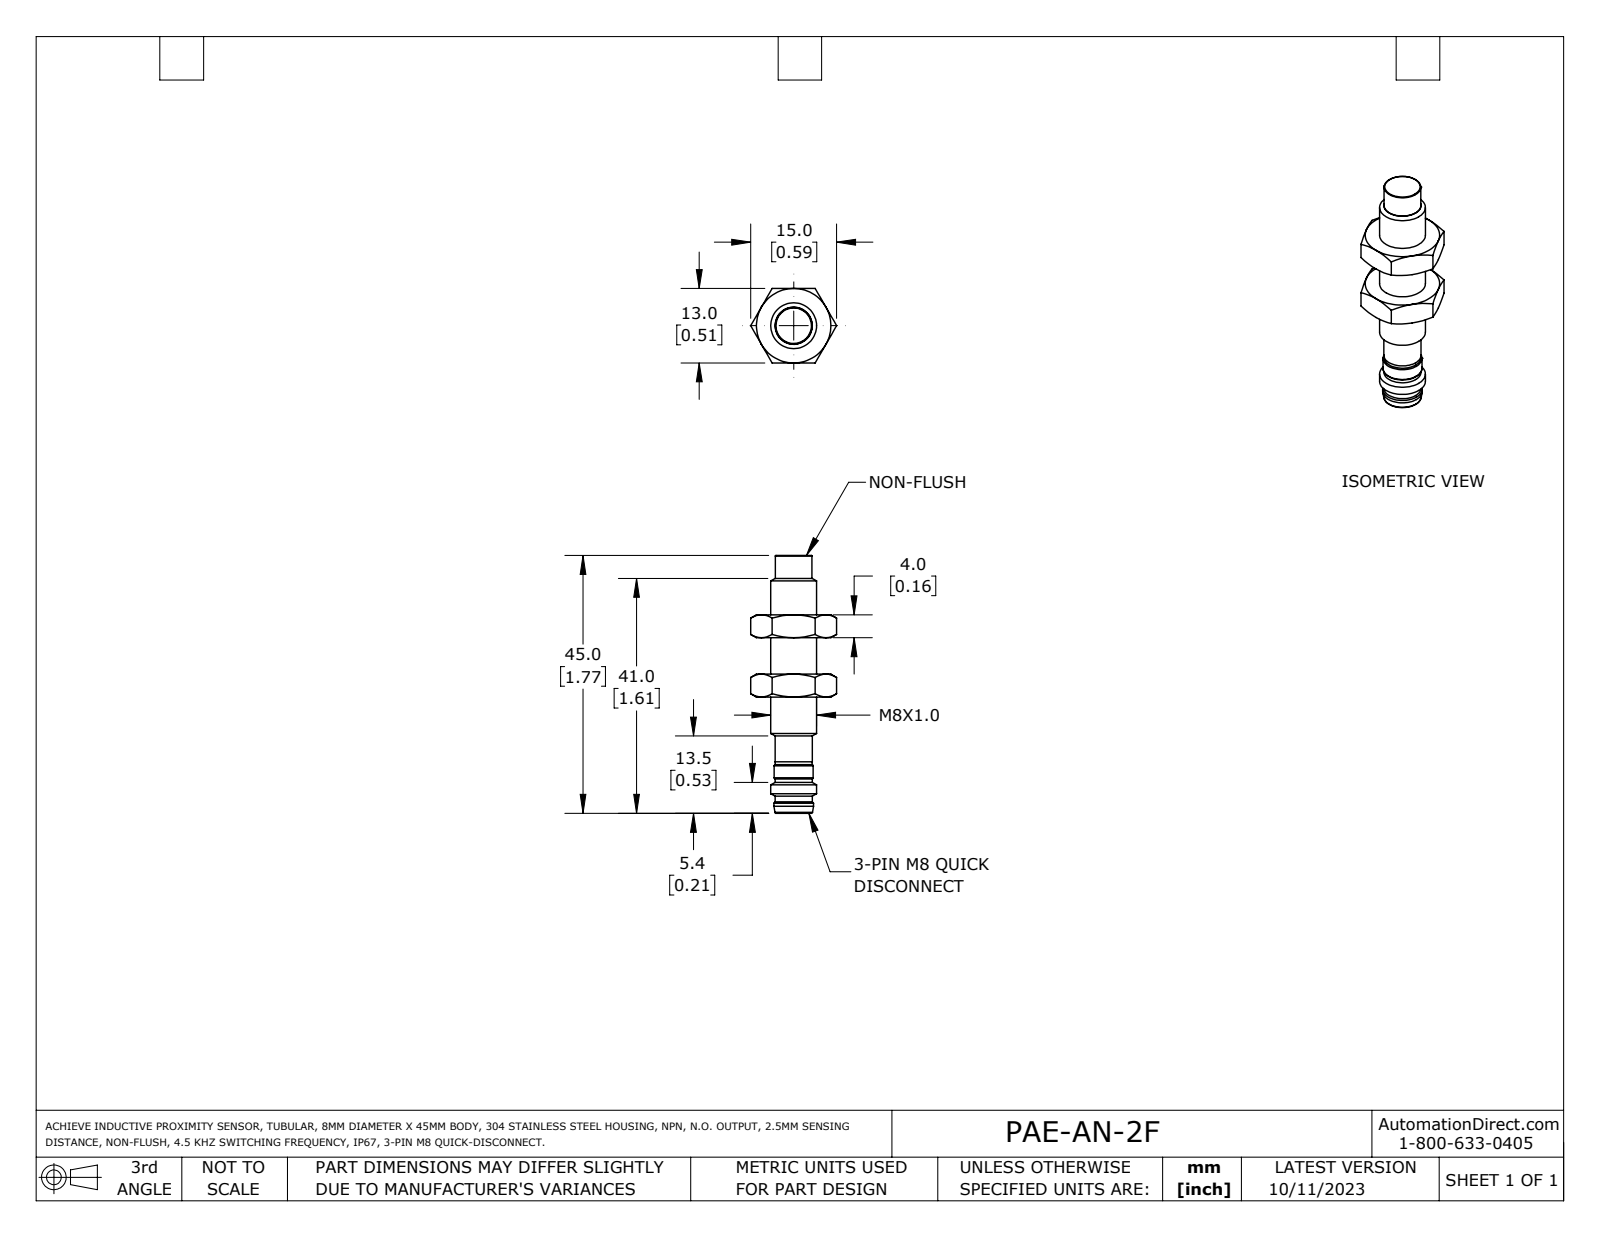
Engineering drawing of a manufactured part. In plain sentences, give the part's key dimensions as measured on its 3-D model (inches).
The part is named "PAE-AN-2F". Its 3-D file was written by "SolidWorks 2023 (AUTOMOTIVE_DESIGN)". It is 3 solids with 76 faces: 26 planar, 15 cylindrical and 35 other. Overall it measures 1.772 by 0.591 by 0.512 inches. Its volume is 0.161 cubic inches and its surface area 3.438 square inches. Round holes: 1 of diameter 0.228, 1 of diameter 0.315. Round bosses or shafts: 3 of diameter 0.039, 1 of diameter 0.272, 1 of diameter 0.268, 1 of diameter 0.256, 1 of diameter 0.254, 1 of diameter 0.252. The main face-to-face distances are 0.407, 0.157, 0.512, 0.565, 0.25, 0.815, 0.972, 0.602, 1.01, 0.76.
